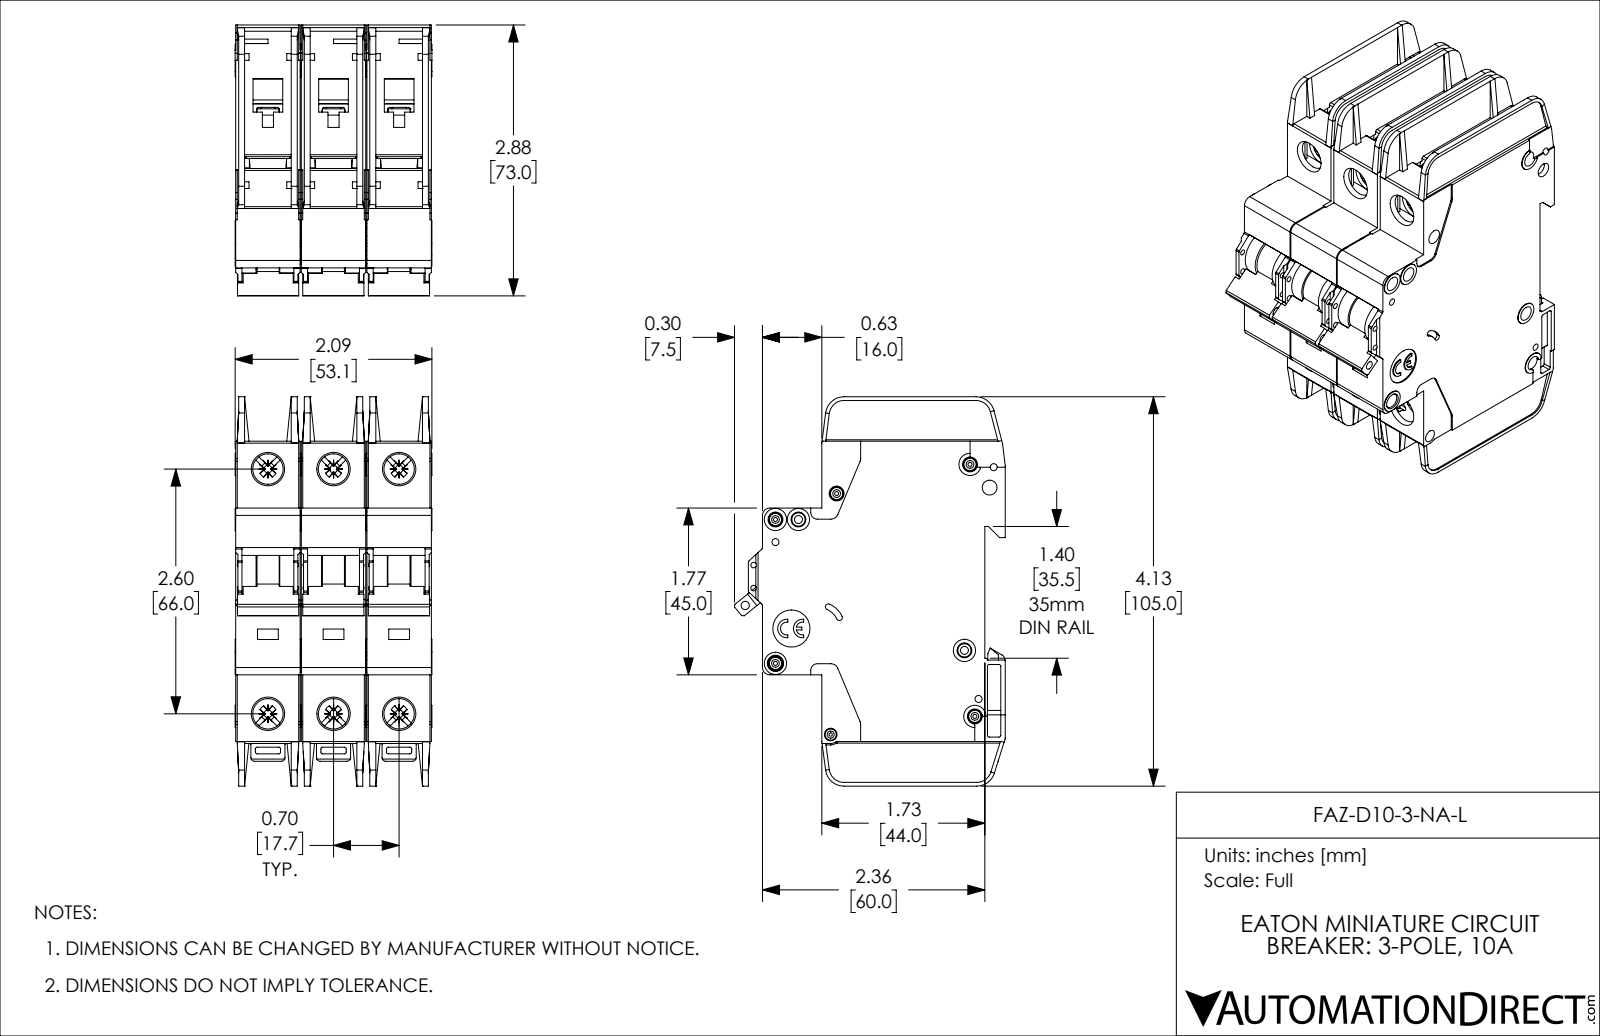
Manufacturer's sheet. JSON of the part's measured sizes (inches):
{"part_name": "FAZ-D10-3-NA-L", "step_written_by": "SolidWorks 2019 (AUTOMOTIVE_DESIGN)", "units": "inches", "bodies": {"solids": 3, "faces": 3381, "planar": 2013, "cylindrical": 1071, "other": 297}, "overall_size": [4.134, 2.876, 2.091], "volume_in3": 14.05, "surface_area_in2": 123, "round_holes": [[0.157, 8], [0.323, 6], [0.043, 5], [0.075, 4], [0.059, 2], [0.085, 2], [0.035, 1], [0.089, 1], [0.098, 1], [0.134, 1], [0.394, 1]], "round_bosses_or_shafts": [[0.13, 5], [0.236, 4], [0.118, 4], [0.098, 3]], "partial_cylinders_radius": [[0.02, 72], [0.016, 30], [0.039, 18], [0.043, 12], [0.079, 12], [0.008, 6], [0.01, 6], [0.028, 6]], "face_to_face_distances": [0.697, 0.047, 1.394, 0.685, 0.591, 1.382, 0.744, 0.65, 0.106, 0.094], "hole_center_spacings": [0.697, 2.69, 2.598, 0.244, 0.537, 0.87, 1.394, 2.948]}
